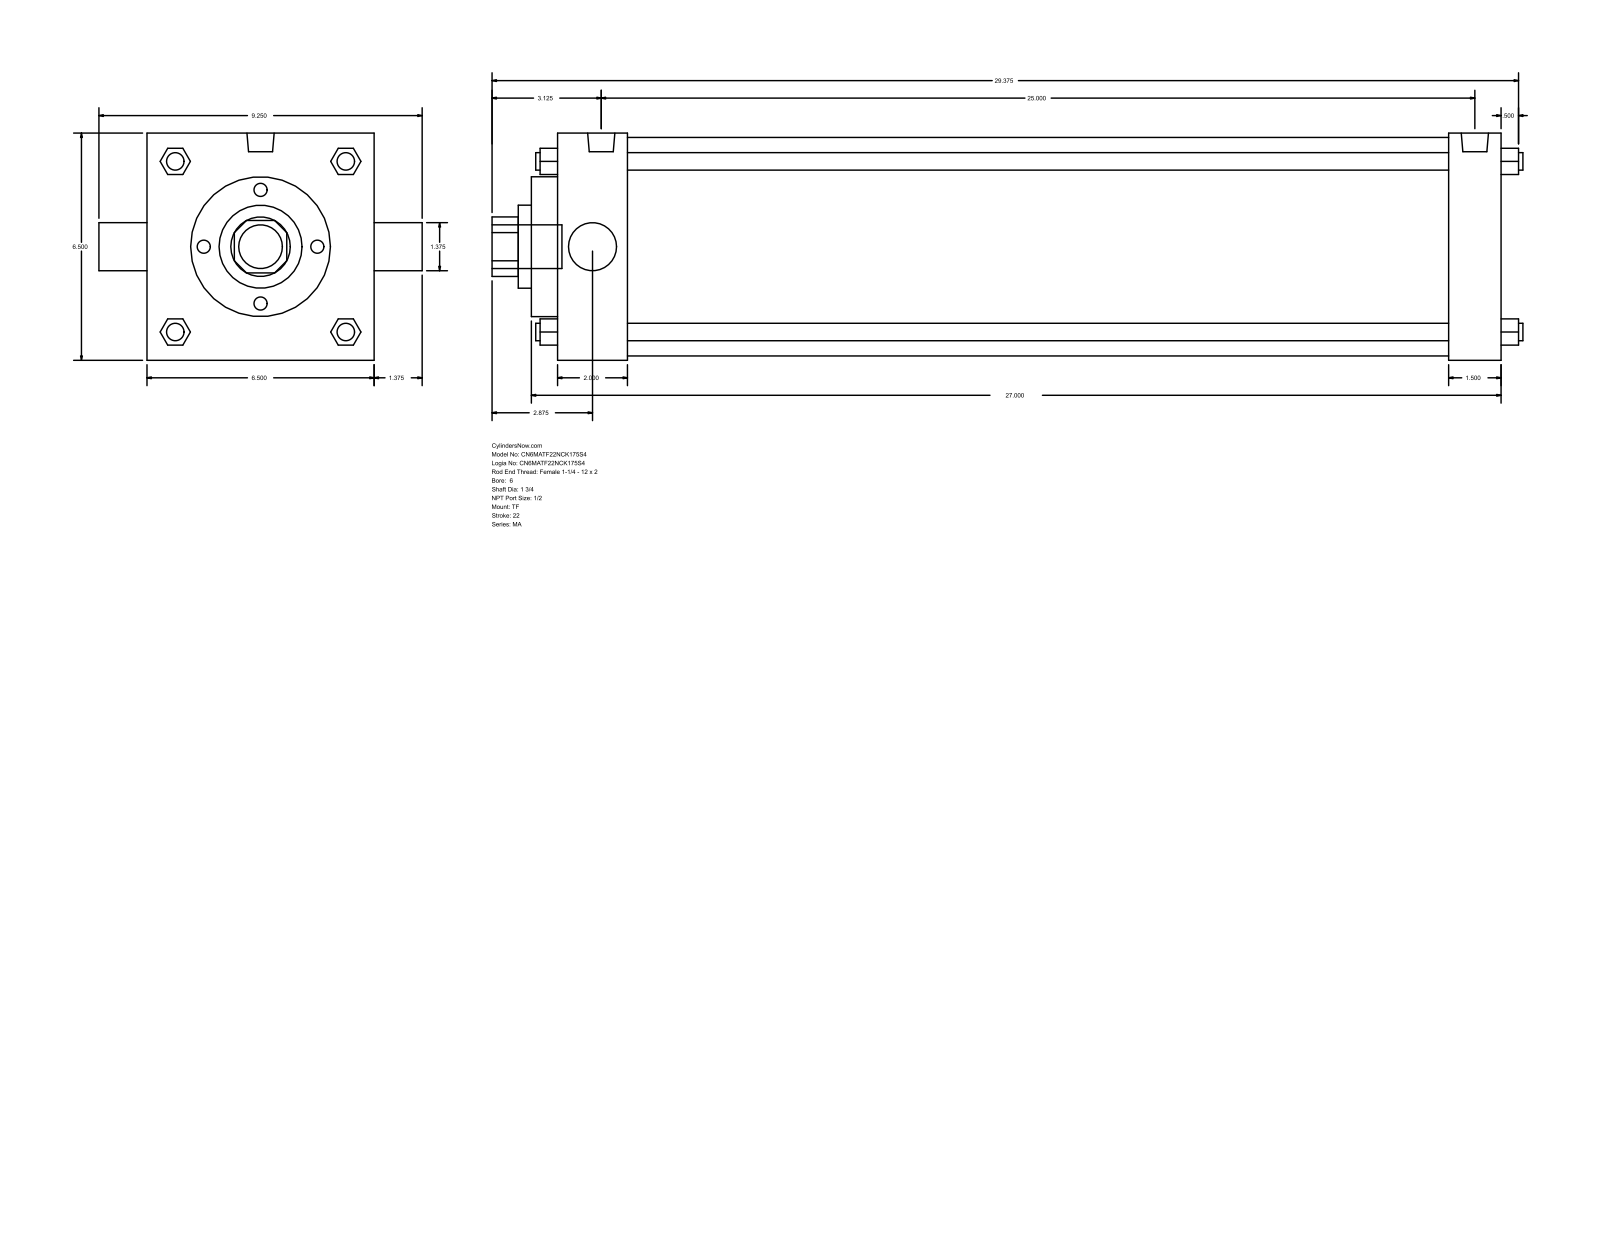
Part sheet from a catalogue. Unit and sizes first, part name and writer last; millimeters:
Units: millimetres
Overall size (bounding box): 749.3 × 234.95 × 165.1
Round holes (diameter × count): ⌀34.92 ×1, ⌀44.45 ×1, ⌀60.33 ×1, ⌀101.6 ×1, ⌀158.75 ×1
Round bosses / shafts (diameter × count): ⌀12.7 ×4, ⌀17.46 ×3, ⌀19.77 ×2, ⌀31.75 ×1
Partial cylindrical surfaces — rounded edges, fillets, slot ends (radius × count): R21.63 ×1
Main face-to-face distances: 165.1, 685.8, 19.05, 50.8, 635, 647.71, 596.91, 38.09, 69.85, 666.76
Bodies: 0 solids, 122 faces (93 planar, 29 cylindrical, 0 other)
Part name (STEP PRODUCT): MA_TF__0600_1.75
STEP written by: GSSL Pune (CONFIG_CONTROL_DESIGN)
